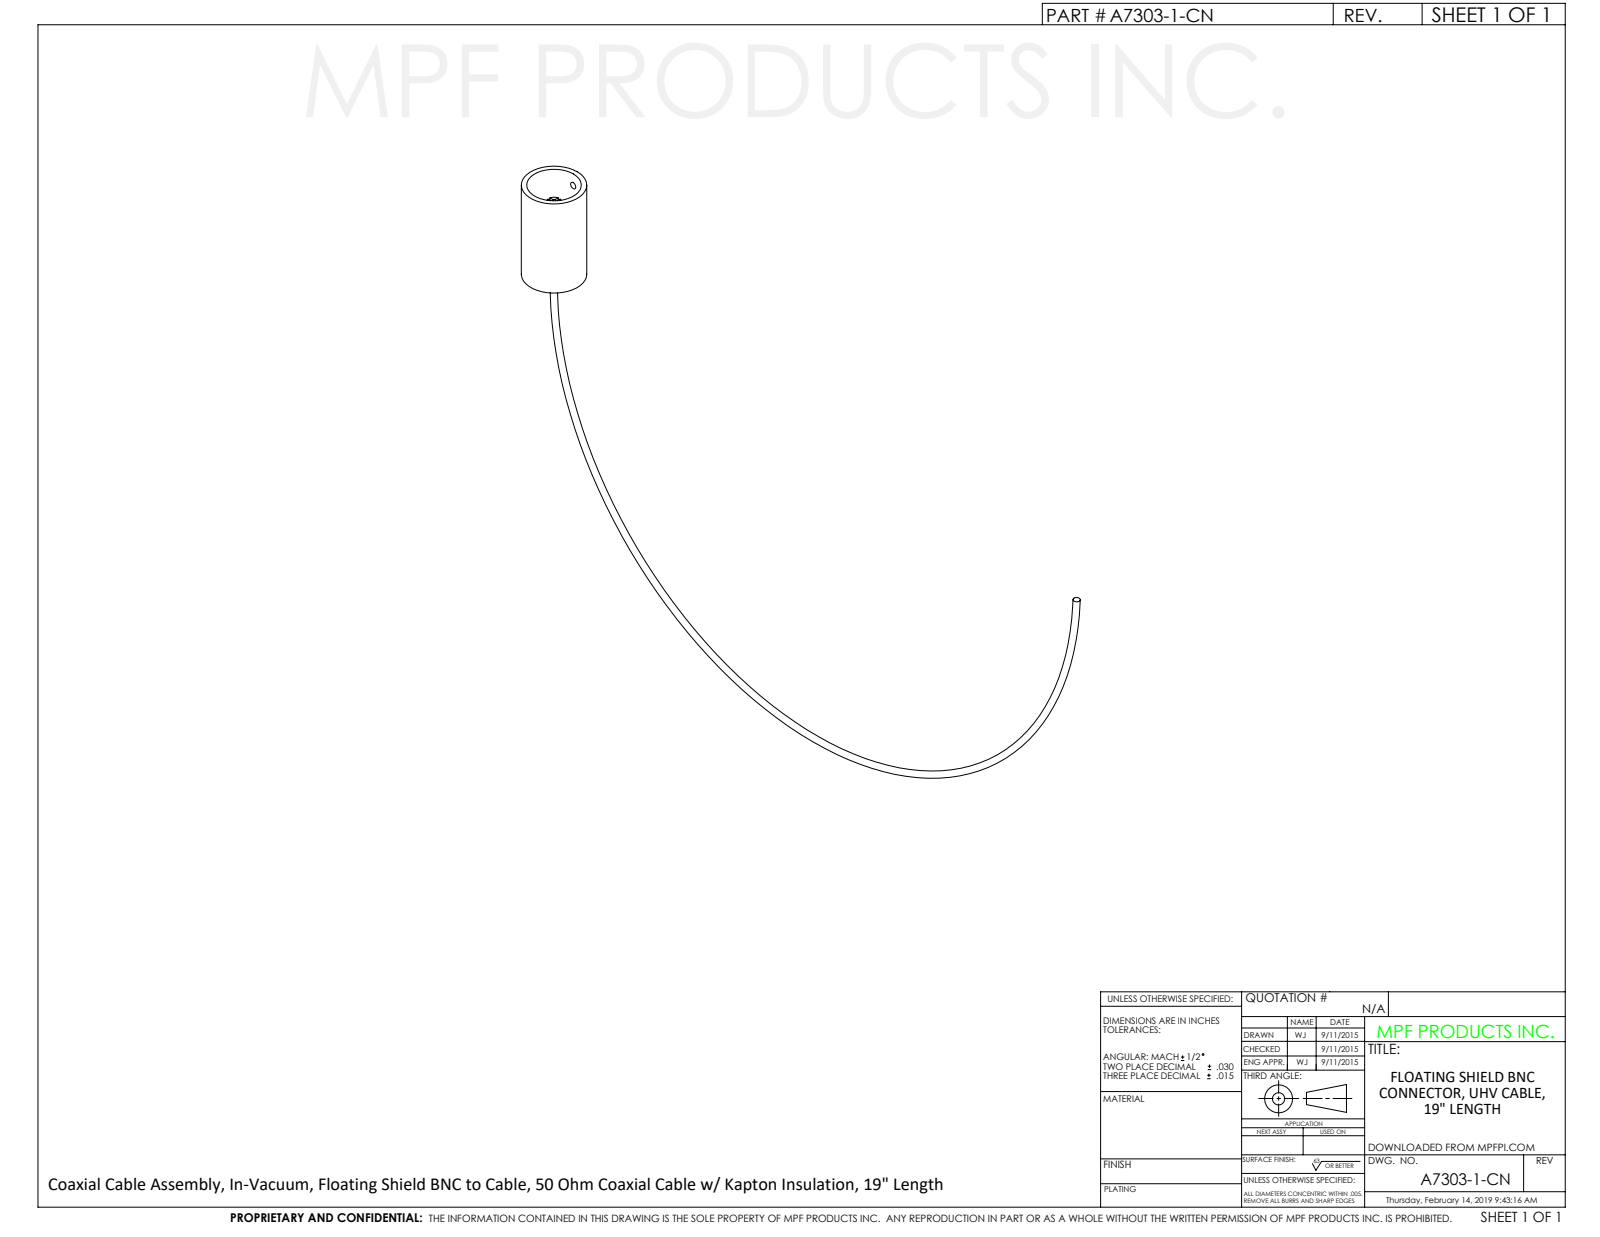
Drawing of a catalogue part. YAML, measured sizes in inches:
part_name: "A7303-1-CN"
step_written_by: "SolidWorks 2012 (CONFIG_CONTROL_DESIGN)"
units: inches
bodies: {solids: 1, faces: 47, planar: 22, cylindrical: 20, other: 5}
overall_size: [10.712, 6.833, 1]
volume: 0.992
surface_area: 13.71
round_holes:
  - {diameter: 0.1, count: 3}
  - {diameter: 0.2, count: 1}
  - {diameter: 0.75, count: 1}
round_bosses_or_shafts:
  - {diameter: 1, count: 1}
  - {diameter: 0.2, count: 1}
face_to_face_distances: [1.5, 0.04, 0.02, 1.252, 0.248, 0.42, 0.38, 1.002, 0.25, 0.498]
hole_center_spacings: [0.35]
